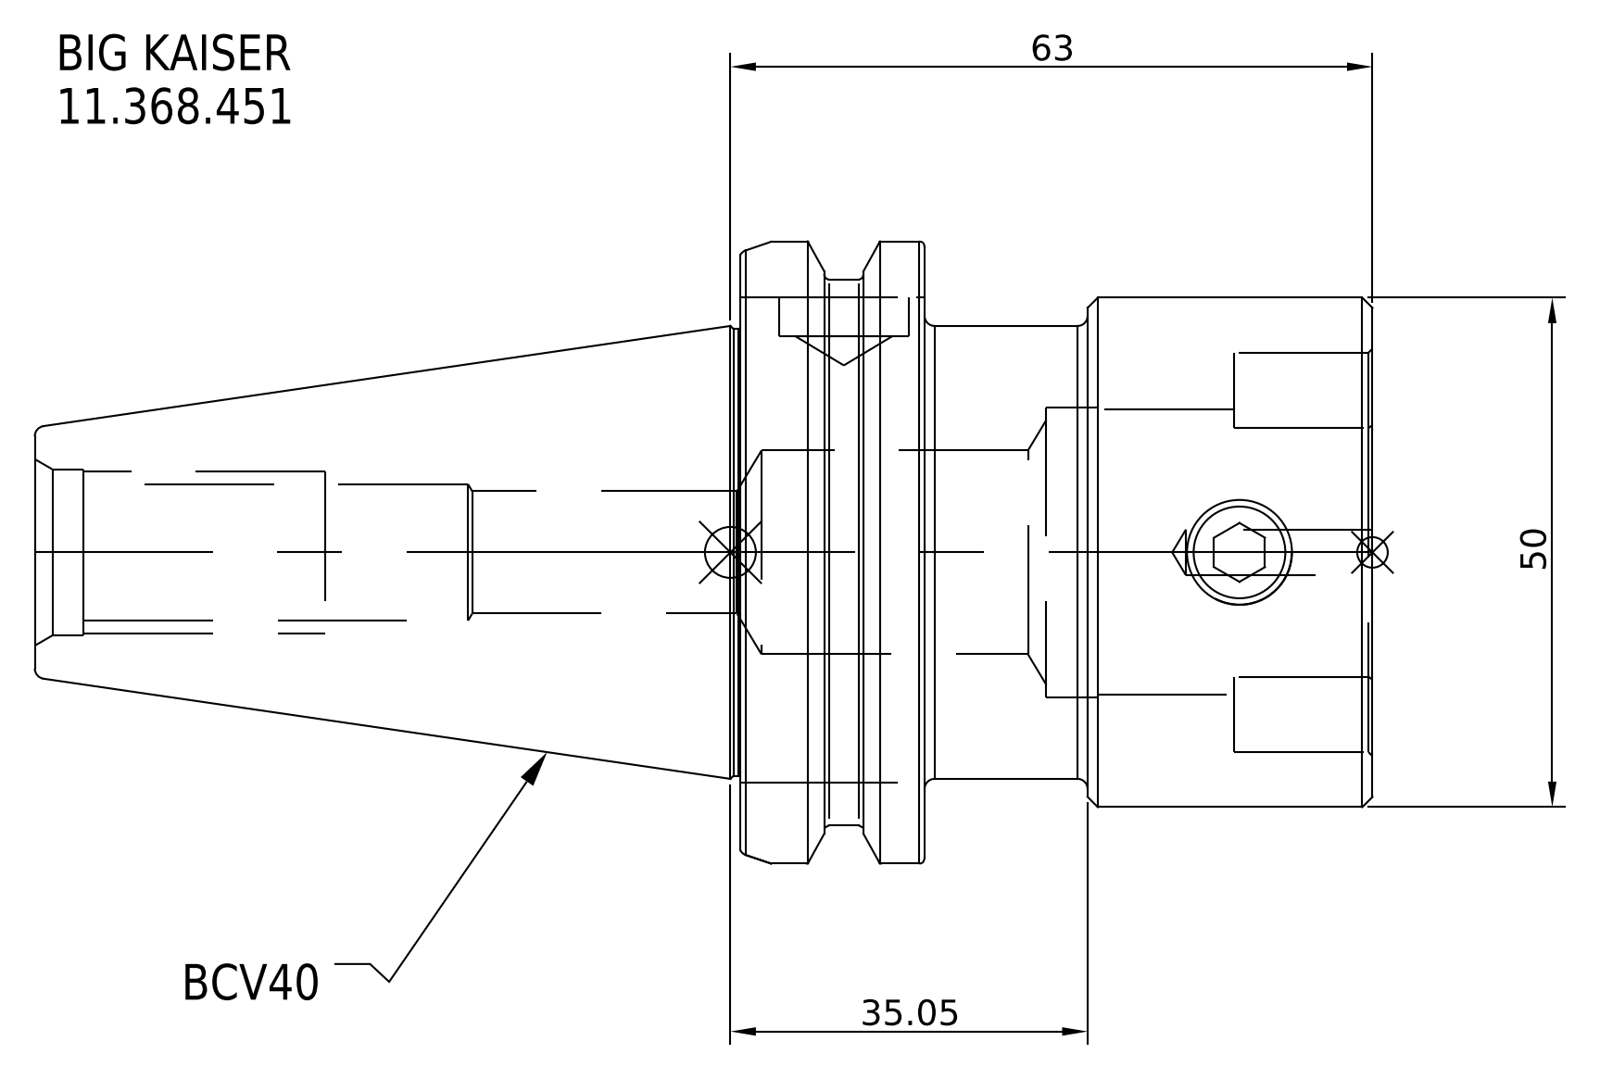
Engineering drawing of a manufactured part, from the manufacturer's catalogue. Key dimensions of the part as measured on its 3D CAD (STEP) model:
Part name (STEP PRODUCT): 11.368.451
STEP written by: SolidWorks 2021 (CONFIG_CONTROL_DESIGN)
Units: millimetres
Bodies: 1 solid, 16 faces (7 planar, 6 cylindrical, 3 other)
Overall size (bounding box): 131.25 × 63.5 × 63.5
Volume: 197 024 mm³ · Surface area: 24 572 mm²
Round bosses / shafts (diameter × count): ⌀63.5 ×1, ⌀56.36 ×1, ⌀50 ×1, ⌀44.45 ×1
Main face-to-face distances: 59.83, 43.95, 15.88, 131.25, 87.3, 71.42, 27.95, 16, 31.88, 103.3
